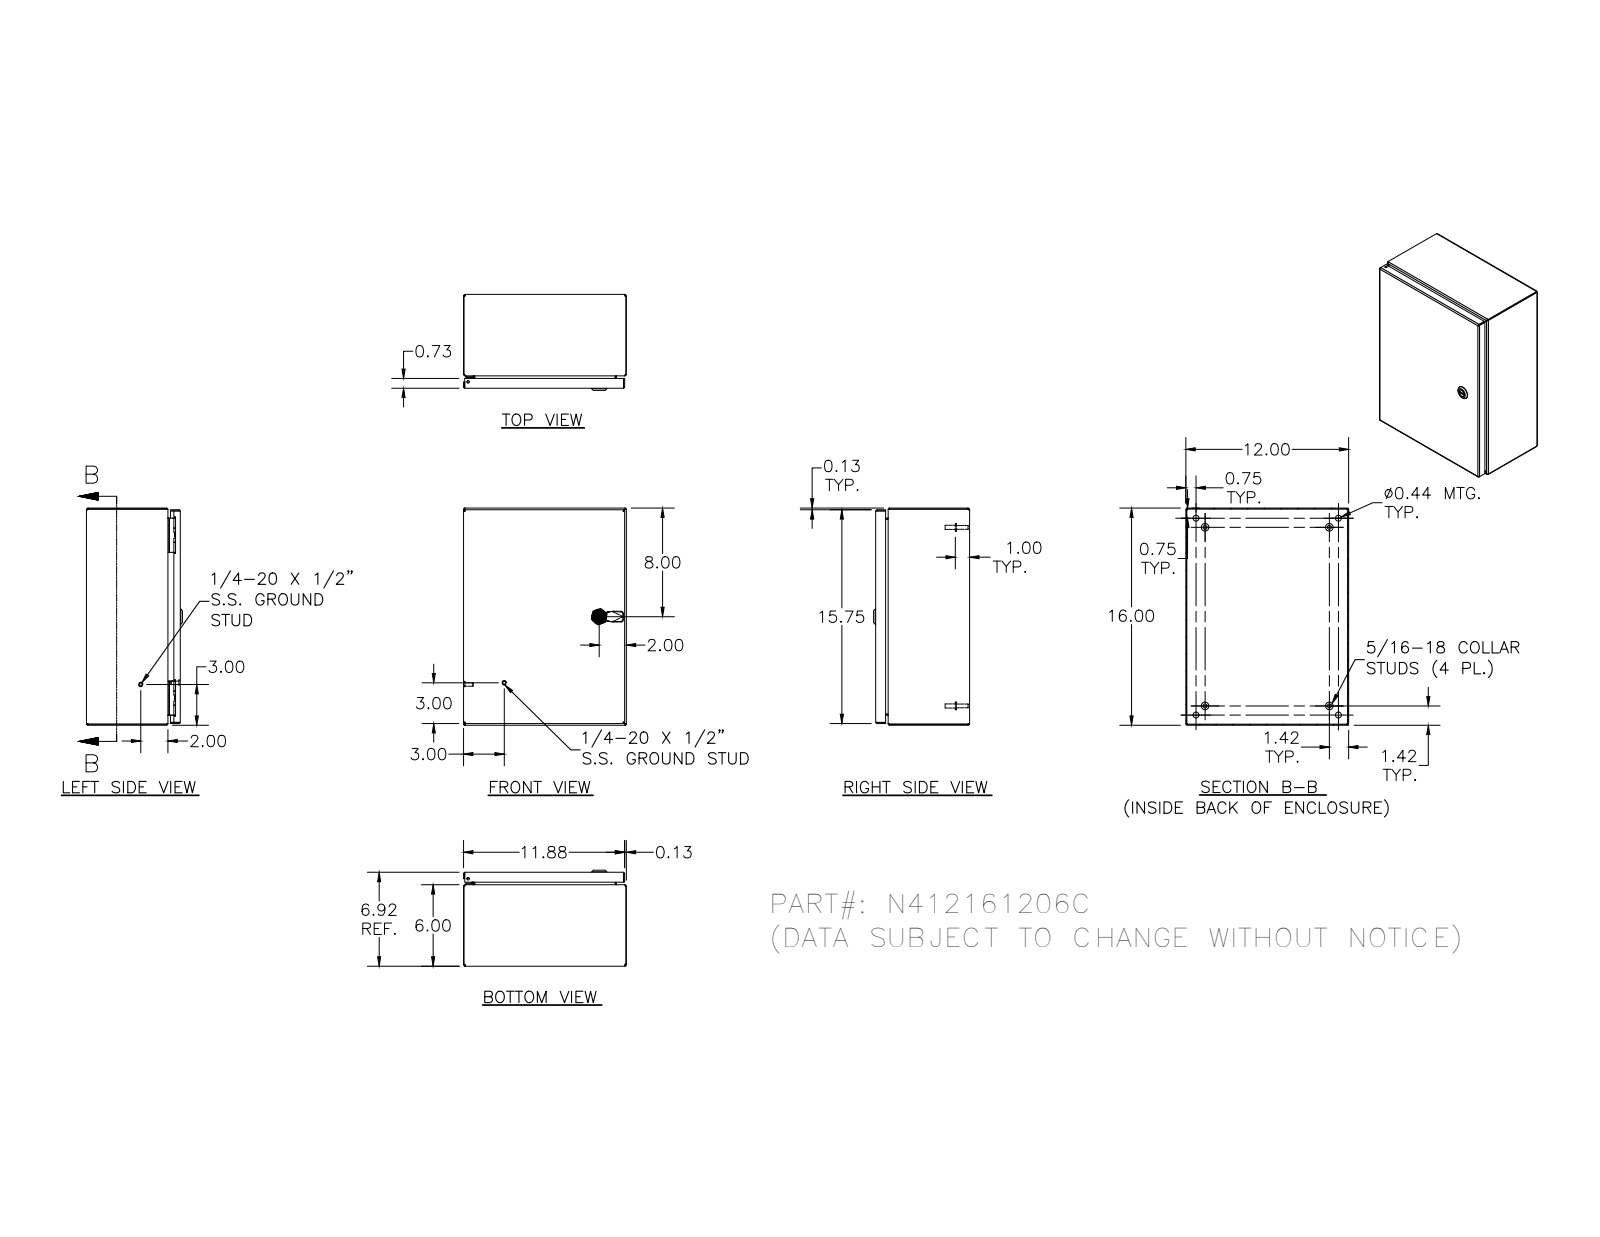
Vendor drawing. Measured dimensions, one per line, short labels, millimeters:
name: N412161206C
written by: SolidWorks 2018 (AUTOMOTIVE_DESIGN)
unit: mm
bodies: 33 solids, 1449 faces (530 planar, 547 cylindrical, 372 other)
size: 406.4 × 304.8 × 179.7
volume: 1 020 000 mm³; area: 1 095 000 mm²
holes: 5× ⌀4.8, 4× ⌀2.4, 4× ⌀3.9, 4× ⌀4.2, 4× ⌀4.4, 4× ⌀11.1, 2× ⌀4, 1× ⌀4.7, 1× ⌀5, 1× ⌀8, 1× ⌀10, 1× ⌀10.2
bosses: 10× ⌀6.4, 4× ⌀14.3, 4× ⌀9.1, 4× ⌀8.1, 4× ⌀7.6, 4× ⌀7, 4× ⌀6.5, 4× ⌀4.2
rounds: 30× R0.3, 30× R0.8, 26× R1.3, 20× R2.7, 18× R0.4, 16× R3.2, 13× R0.5, 8× R0.8
face distances: 1.9, 173.8, 171.9, 175.7, 1.9, 302.9, 304.8, 301, 302.9, 404.5
hole spacings: 304.8, 16.8, 16.7, 33.2, 49.9, 12.7, 25, 33.3
